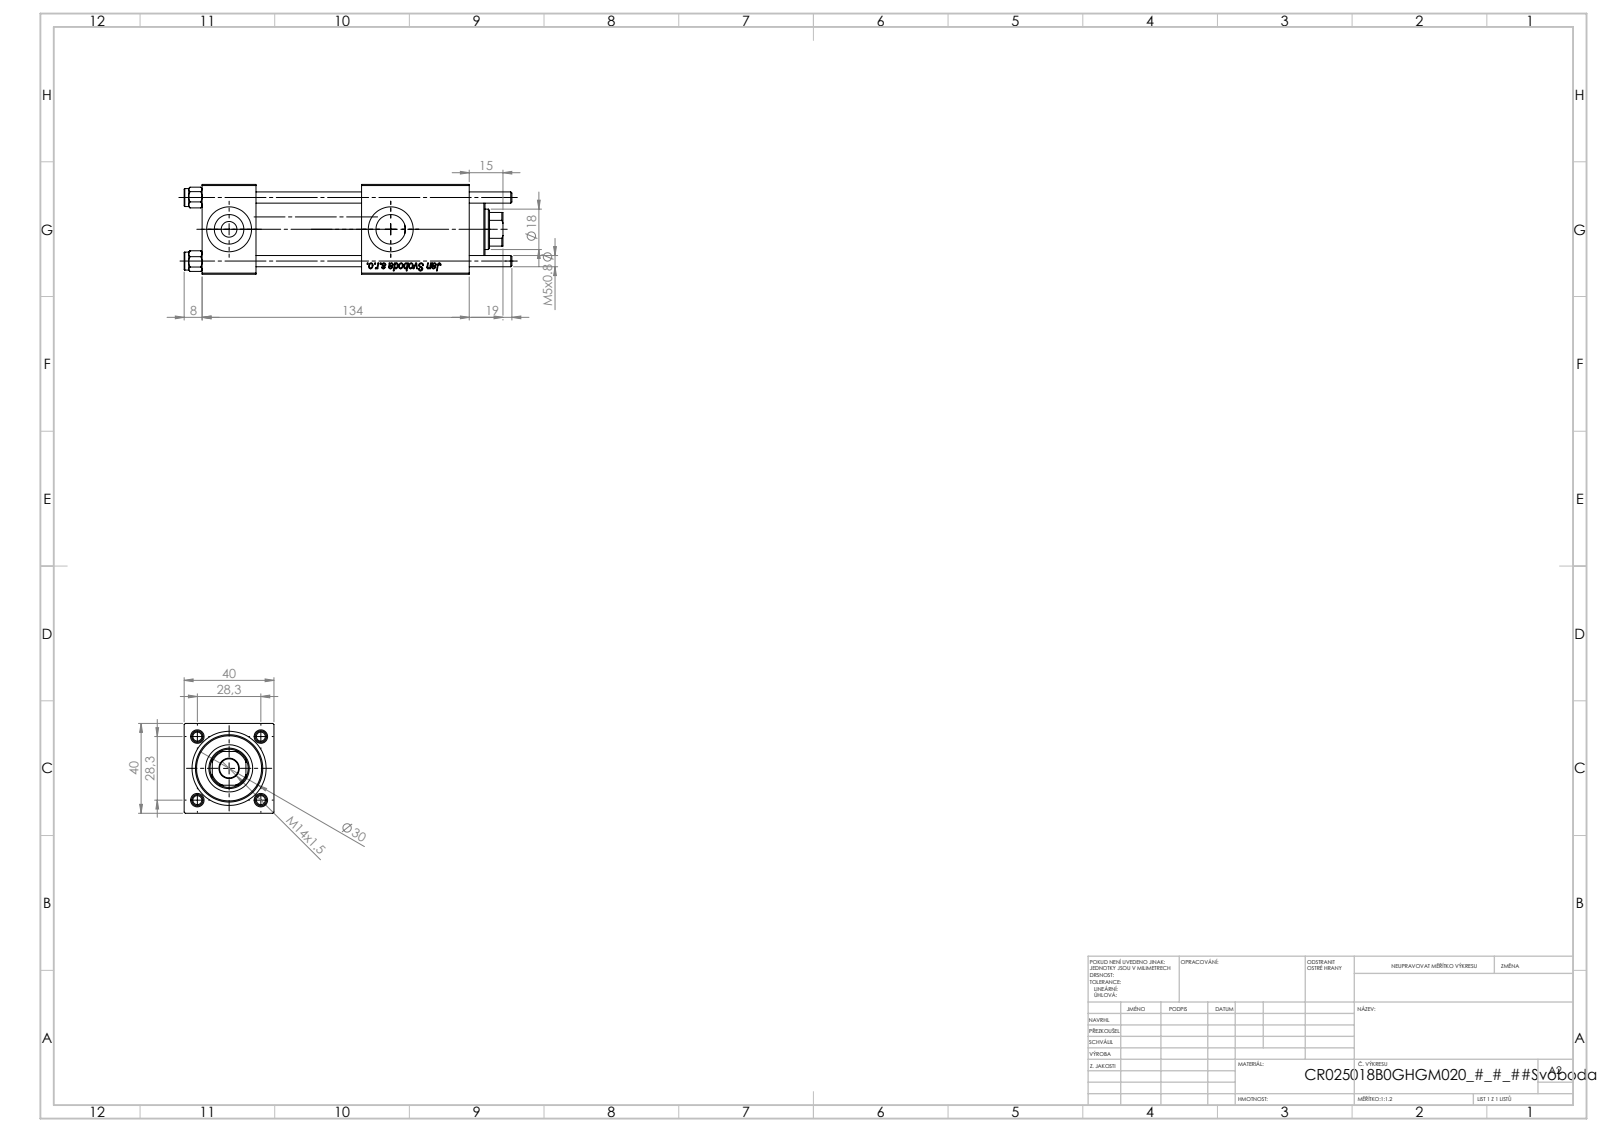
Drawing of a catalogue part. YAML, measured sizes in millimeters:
part_name: "V215CR_B_TYCINKA; V215_VC_A; V215CR_VCP_B; NUT_M5_B (+1 more)"
step_written_by: "SolidWorks 2019 (CONFIG_CONTROL_DESIGN)"
units: millimeters
bodies: {solids: 11, faces: 1152, planar: 428, cylindrical: 76, other: 648}
overall_size: [146, 40, 40]
volume: 152491
surface_area: 60895
round_holes:
  - {diameter: 5, count: 4}
  - {diameter: 20, count: 3}
  - {diameter: 7, count: 2}
  - {diameter: 13.16, count: 2}
  - {diameter: 8.5, count: 1}
  - {diameter: 18, count: 1}
  - {diameter: 21, count: 1}
  - {diameter: 25, count: 1}
  - {diameter: 30, count: 1}
round_bosses_or_shafts:
  - {diameter: 8, count: 4}
  - {diameter: 31, count: 1}
partial_cylinders:
  - {radius: 8.5, count: 1}
face_to_face_distances: [40, 24, 71, 47, 90.3, 66.3, 19.3, 119, 95, 48]
hole_center_spacings: [20.01, 28.3, 40.02, 72]
